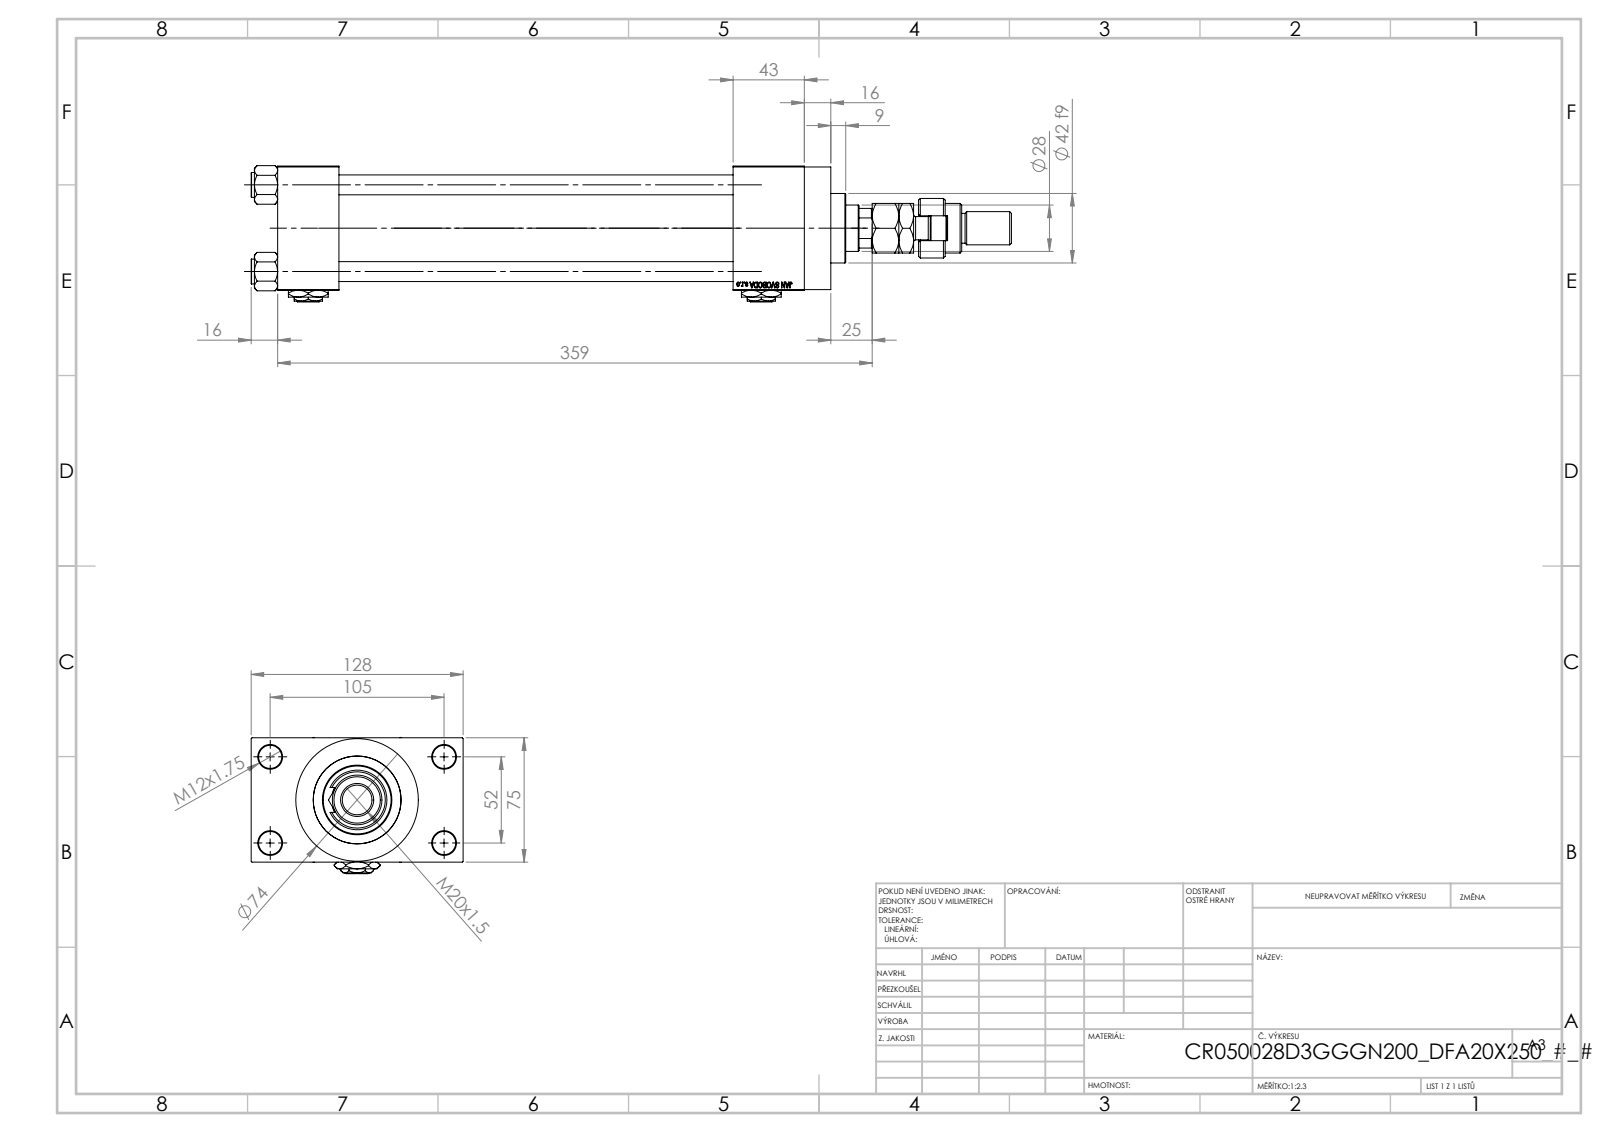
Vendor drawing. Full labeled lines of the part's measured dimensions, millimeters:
Part name (STEP PRODUCT): V215CR_VCP_D; NUT_M5_D; Zatka_pro_OIL_PORT; FEMALE_PART_FOR_DFA (+4 more)
STEP written by: SolidWorks 2019 (CONFIG_CONTROL_DESIGN)
Units: millimetres
Bodies: 15 solids, 1290 faces (573 planar, 113 cylindrical, 604 other)
Overall size (bounding box): 459 × 128 × 82.27
Volume: 1 142 000 mm³ · Surface area: 289 265 mm²
Round holes (diameter × count): ⌀12 ×4, ⌀14 ×4, ⌀7 ×2, ⌀20.96 ×2, ⌀30 ×2, ⌀18.5 ×1, ⌀28 ×1, ⌀31 ×1, ⌀41 ×1, ⌀50 ×1, ⌀53 ×1
Round bosses / shafts (diameter × count): ⌀15 ×4, ⌀74 ×1, ⌀56 ×1, ⌀42 ×1, ⌀36 ×1, ⌀30 ×1, ⌀22 ×1, ⌀20 ×1
Partial cylindrical surfaces — rounded edges, fillets, slot ends (radius × count): R7.5 ×1, R12 ×1, R13.5 ×1
Main face-to-face distances: 75, 238, 37, 275, 26.5, 101.5, 43, 318, 281, 16
Hole centre spacings: 26.35, 36.98, 52.3, 58.43, 58.59, 78.65, 94.37, 52
